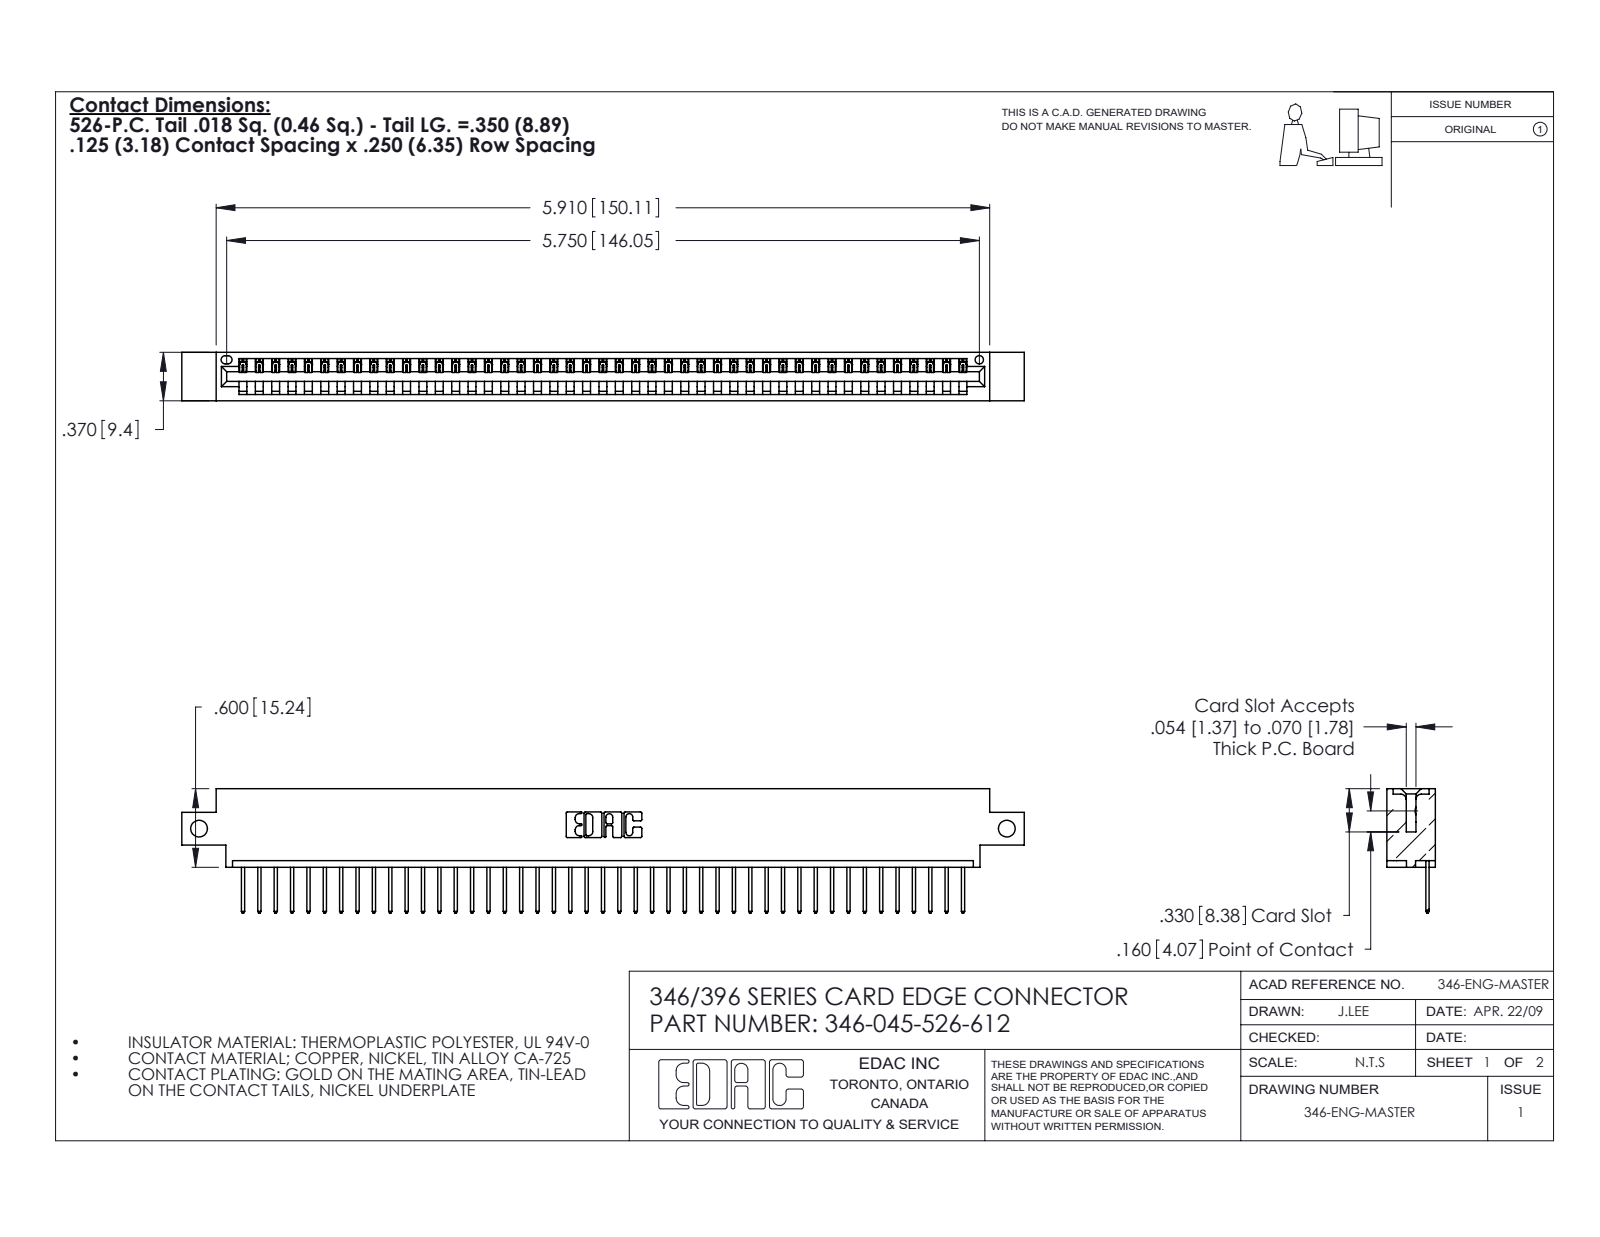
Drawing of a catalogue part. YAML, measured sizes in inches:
part_name: "346-045-526-612; 346 Part_0.170 Offset - Side Mount; 345-292-001_345-293-126"
step_written_by: "SolidWorks 2020 (CONFIG_CONTROL_DESIGN)"
units: inches
bodies: {solids: 46, faces: 2736, planar: 1880, cylindrical: 856, other: 0}
overall_size: [6.435, 0.95, 0.37]
volume: 0.939
surface_area: 29.82
round_holes:
  - {diameter: 0.128, count: 2}
  - {diameter: 0.064, count: 1}
partial_cylinders:
  - {radius: 0.006, count: 90}
  - {radius: 0.01, count: 90}
  - {radius: 0.01, count: 22}
  - {radius: 0.007, count: 6}
  - {radius: 0.031, count: 6}
  - {radius: 0.026, count: 3}
  - {radius: 0.031, count: 2}
  - {radius: 0.04, count: 2}
face_to_face_distances: [0.048, 0.322, 0.37, 0.25, 0.072, 0.298, 0.025, 0.148, 0.222, 0.1]
hole_center_spacings: [6.17]
